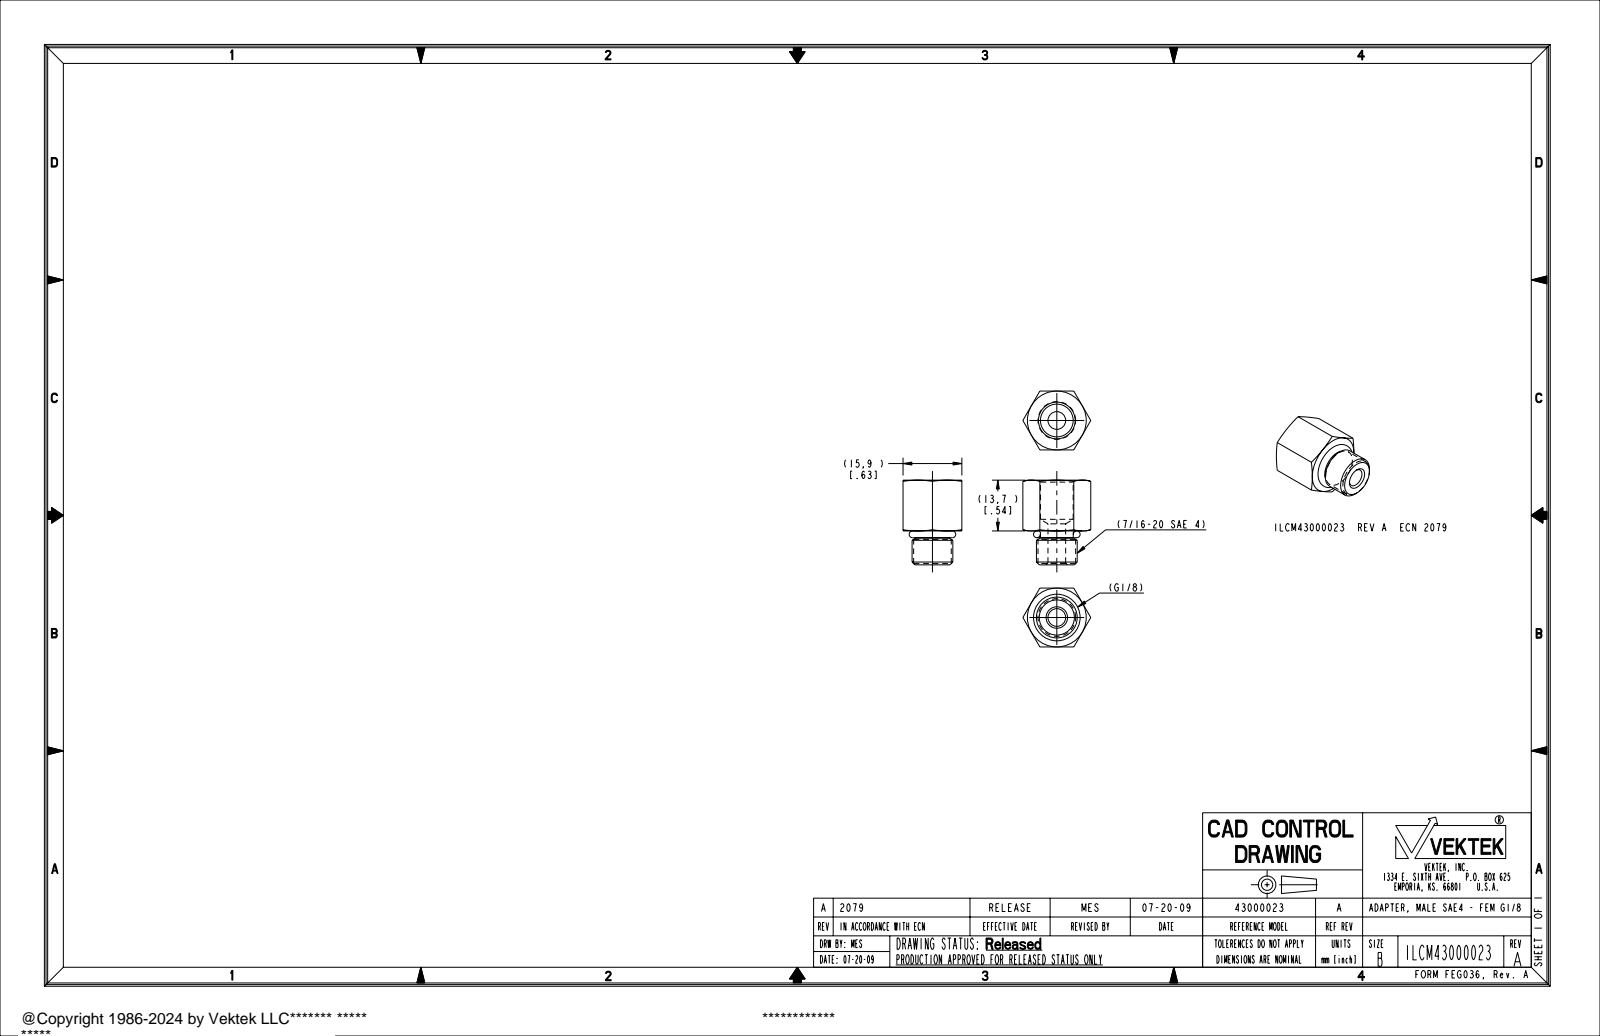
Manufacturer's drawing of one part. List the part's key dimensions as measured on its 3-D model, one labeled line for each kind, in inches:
Part name (STEP PRODUCT): ILCM43000023
STEP written by: PRO/ENGINEER BY PARAMETRIC TECHNOLOGY CORPORATION, 2007460 (AUTOMOTIVE_DESIGN_CC2)
Units: inches
Bodies: 2 solids, 50 faces (10 planar, 12 cylindrical, 28 other)
Overall size (bounding box): 0.899 × 0.722 × 0.625
Volume: 0.181 in³ · Surface area: 4.104 in²
Round holes (diameter × count): ⌀0.188 ×1, ⌀0.348 ×1
Round bosses / shafts (diameter × count): ⌀0.433 ×1, ⌀0.4 ×1, ⌀0.383 ×1, ⌀0.349 ×1
Main face-to-face distances: 0.625, 0.54, 0.36, 0.9, 0.504, 0.144, 0.395
